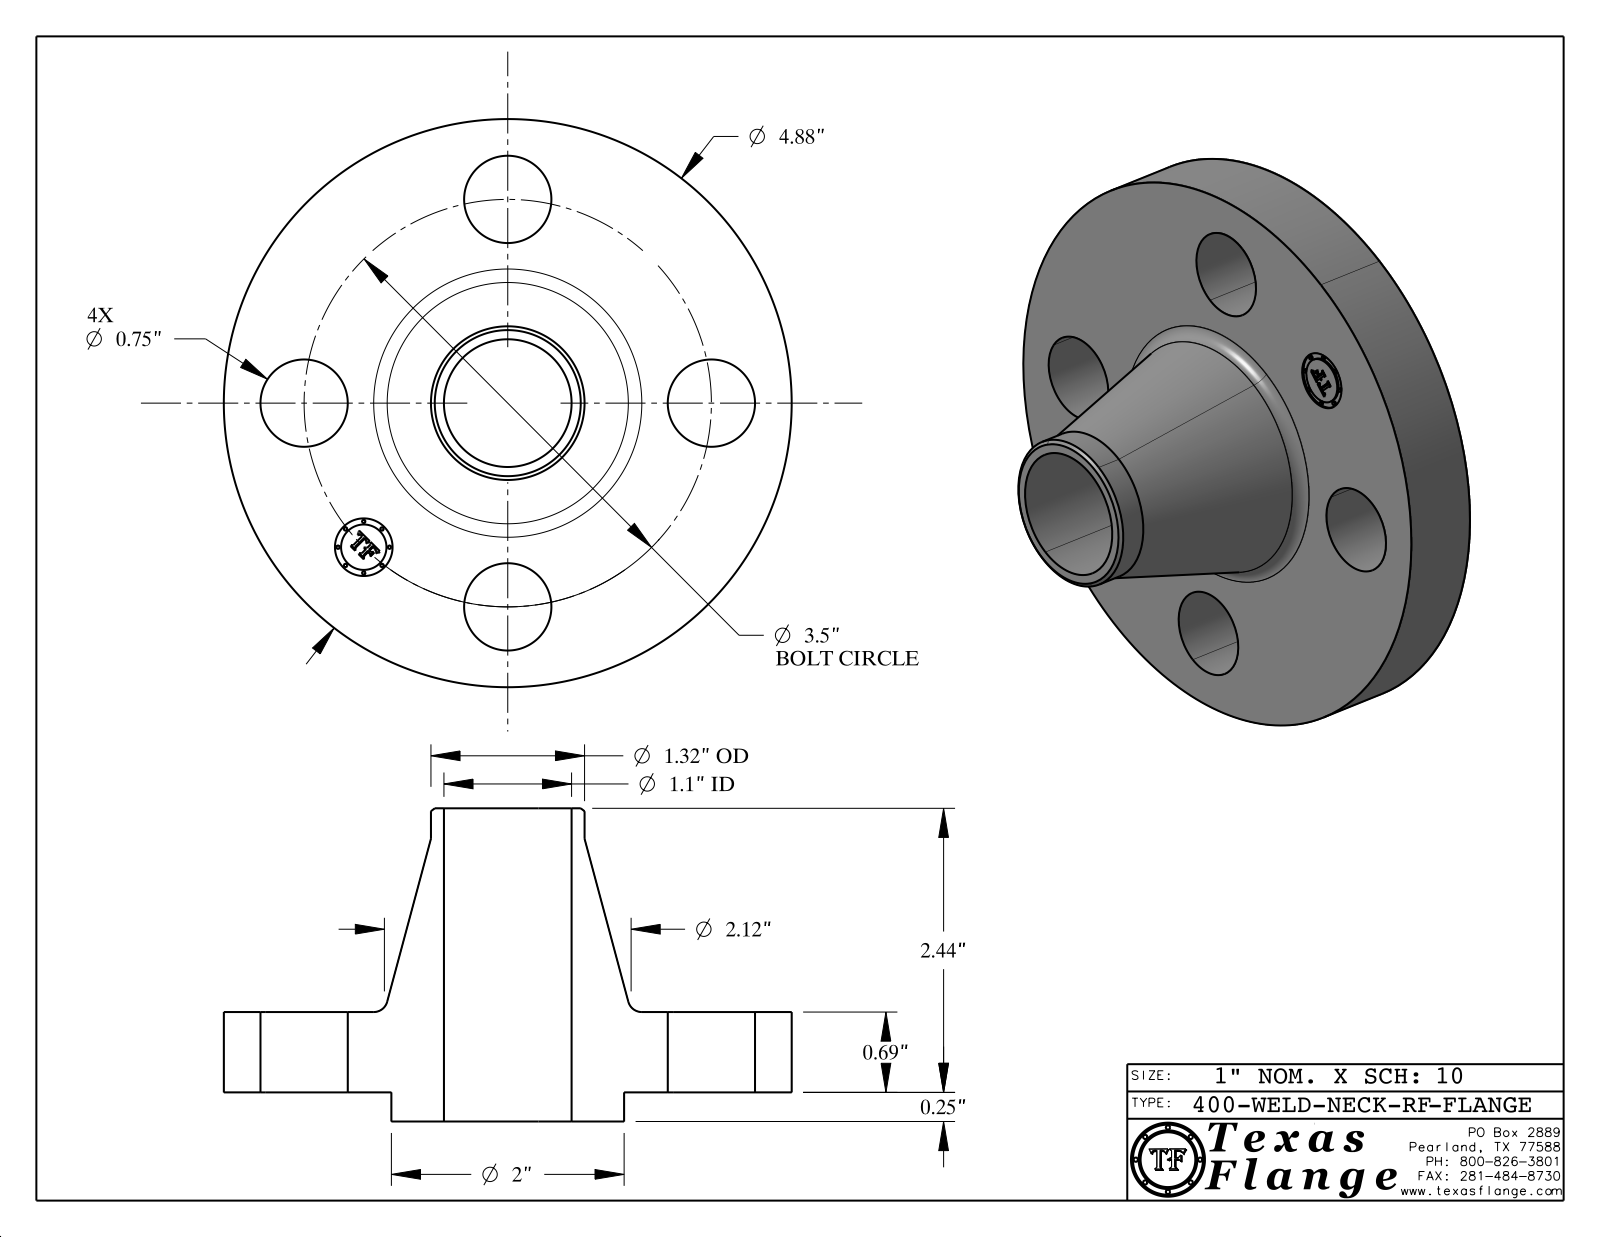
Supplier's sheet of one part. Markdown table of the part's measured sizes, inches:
| quantity | value |
| --- | --- |
| part name | 400-WELD-NECK-RF |
| STEP written by | CATIA V5 STEP AP214 (AUTOMOTIVE_DESIGN) |
| units | inches |
| bodies | 1 solid, 411 faces (369 planar, 36 cylindrical, 6 other) |
| overall size | 4.88 × 4.88 × 2.69 |
| volume | 13.82 in³ |
| surface area | 67.01 in² |
| round holes (diameter × count) | 0.75 × 4, 0.495 × 1, 1.097 × 1 |
| round bosses / shafts (diameter × count) | 0.03 × 8, 4.88 × 1, 2 × 1, 1.32 × 1, 0.39 × 1 |
| main face-to-face distances | 0.69, 0.25, 0.94, 2.69, 2.44, 1.75, 0.015, 0.925, 0.675, 1.765 |
| hole center spacings | 1.75, 2.475, 1.339, 3.233, 3.5 |
